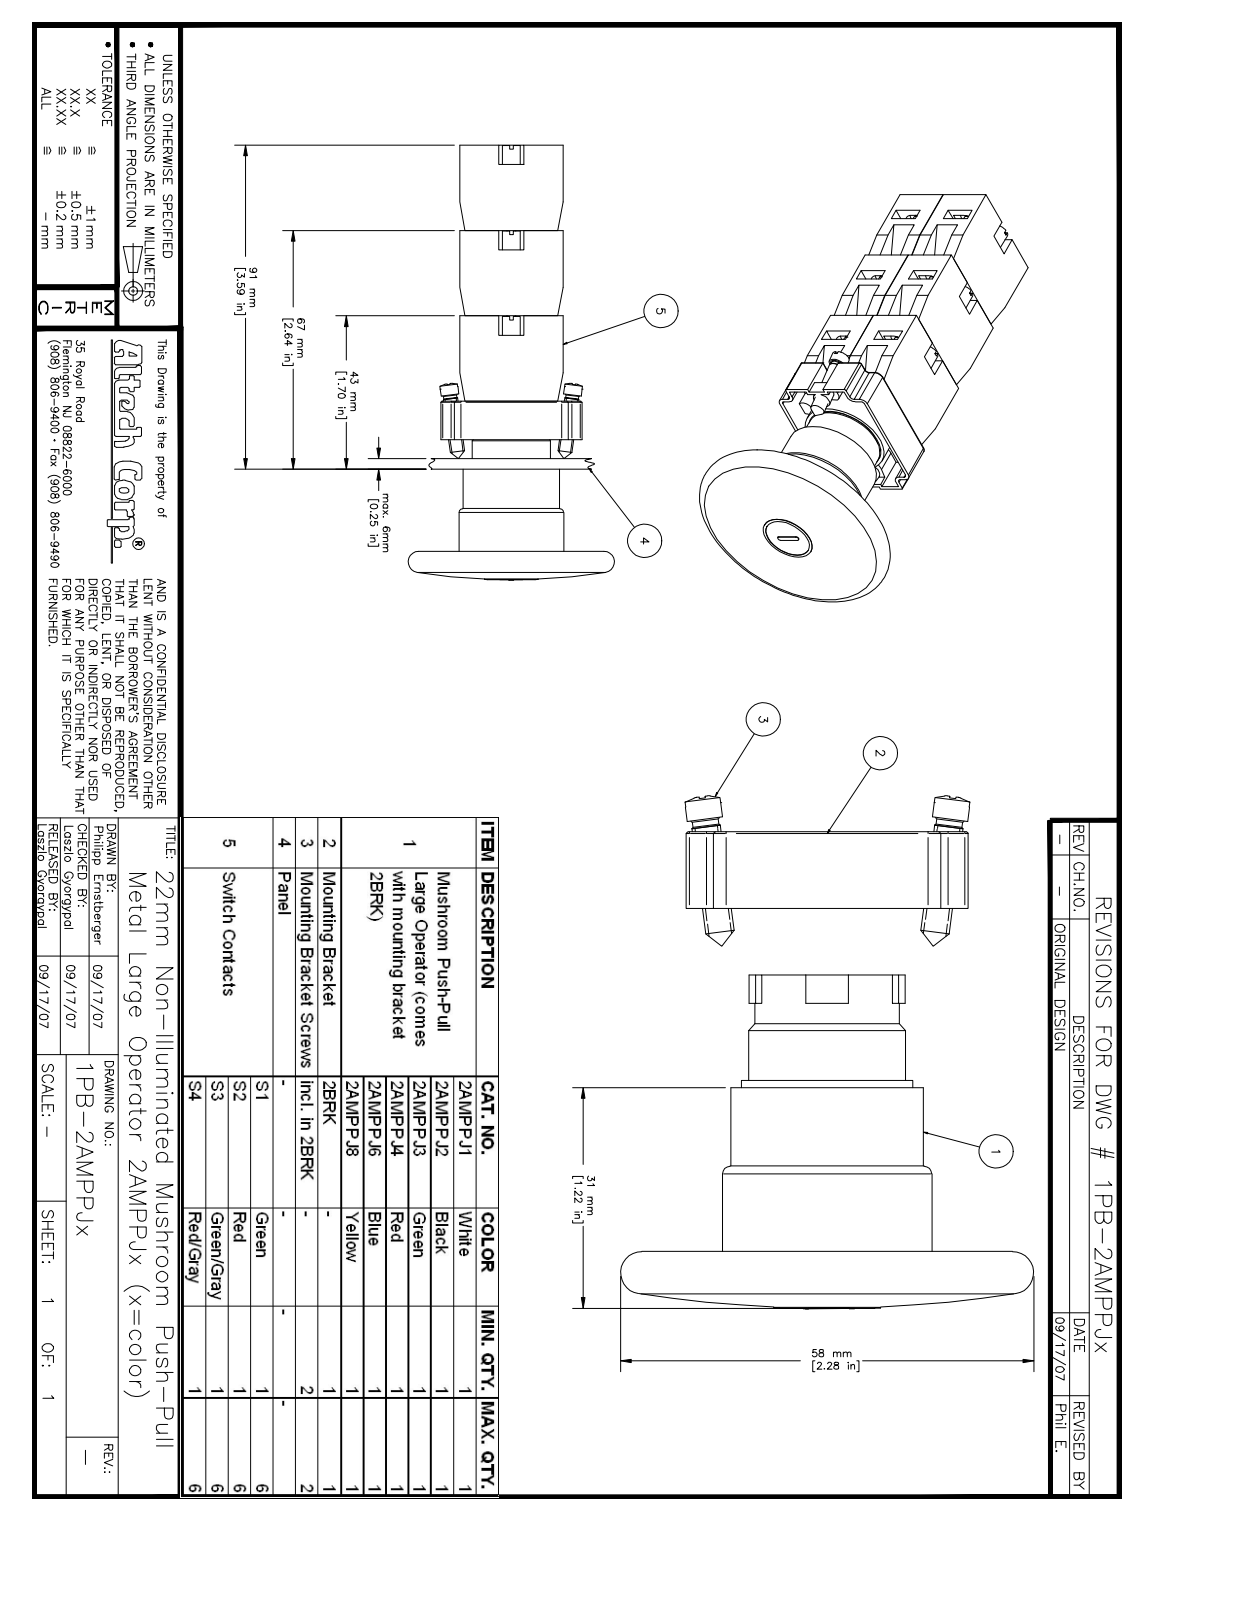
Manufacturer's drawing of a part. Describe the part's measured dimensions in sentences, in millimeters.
The part is named "2AMPPJx_assemlby; 2AMPPJx; rubber_gasket; 2BRK (+6 more)". Its 3-D file was written by "Autodesk Inventor 2008 (AUTOMOTIVE_DESIGN)". It is 30 solids with 1220 faces: 665 planar, 194 cylindrical and 361 other. Overall it measures 122.2 by 60.45 by 58 millimeters. Its volume is 95 472 cubic millimeters and its surface area 51 189 square millimeters. Round holes: 5 of diameter 2.5, 2 of diameter 2.6, 1 of diameter 13.4, 1 of diameter 18, 1 of diameter 22, 1 of diameter 22.25, 1 of diameter 22.5, 1 of diameter 25, 1 of diameter 27.1. Round bosses or shafts: 6 of diameter 3, 4 of diameter 5, 4 of diameter 2.75, 4 of diameter 1.5, 2 of diameter 4, 2 of diameter 3.65, 1 of diameter 29.4, 1 of diameter 27. Partial cylindrical surfaces (rounded edges, fillets, slot ends): 14 of radius 0.25, 13 of radius 1, 8 of radius 0.72, 5 of radius 2.25, 4 of radius 0.5, 4 of radius 0.8, 4 of radius 1.8, 4 of radius 2. The main face-to-face distances are 14.8, 14.7, 24, 3, 29, 29.5, 48, 1, 19.1, 64.1. The hole center spacings are 14.53, 6.52, 6.57, 13, 25.88, 26, 26.27, 29.07.
